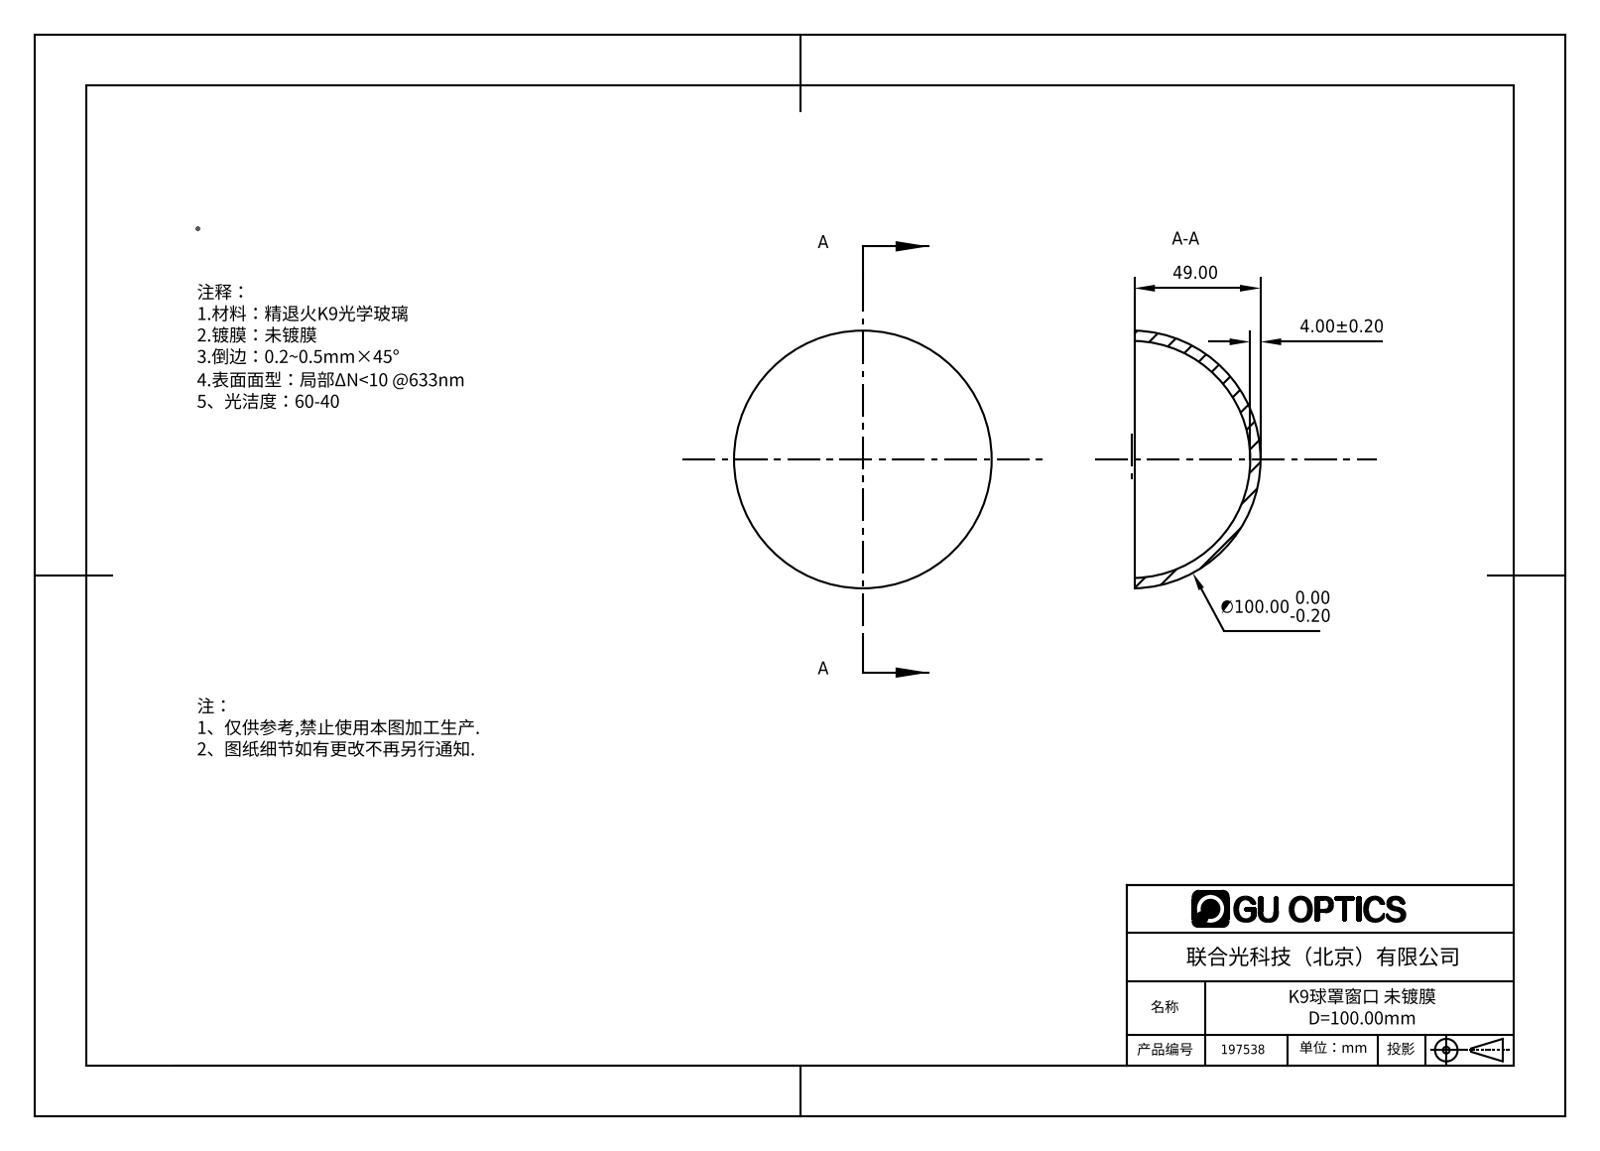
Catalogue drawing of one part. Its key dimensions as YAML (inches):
part_name: "197538"
step_written_by: "SolidWorks 2016 (AUTOMOTIVE_DESIGN)"
units: inches
bodies: {solids: 1, faces: 5, planar: 1, cylindrical: 0, other: 4}
overall_size: [3.936, 3.936, 1.929]
volume: 3.46
surface_area: 45.86
